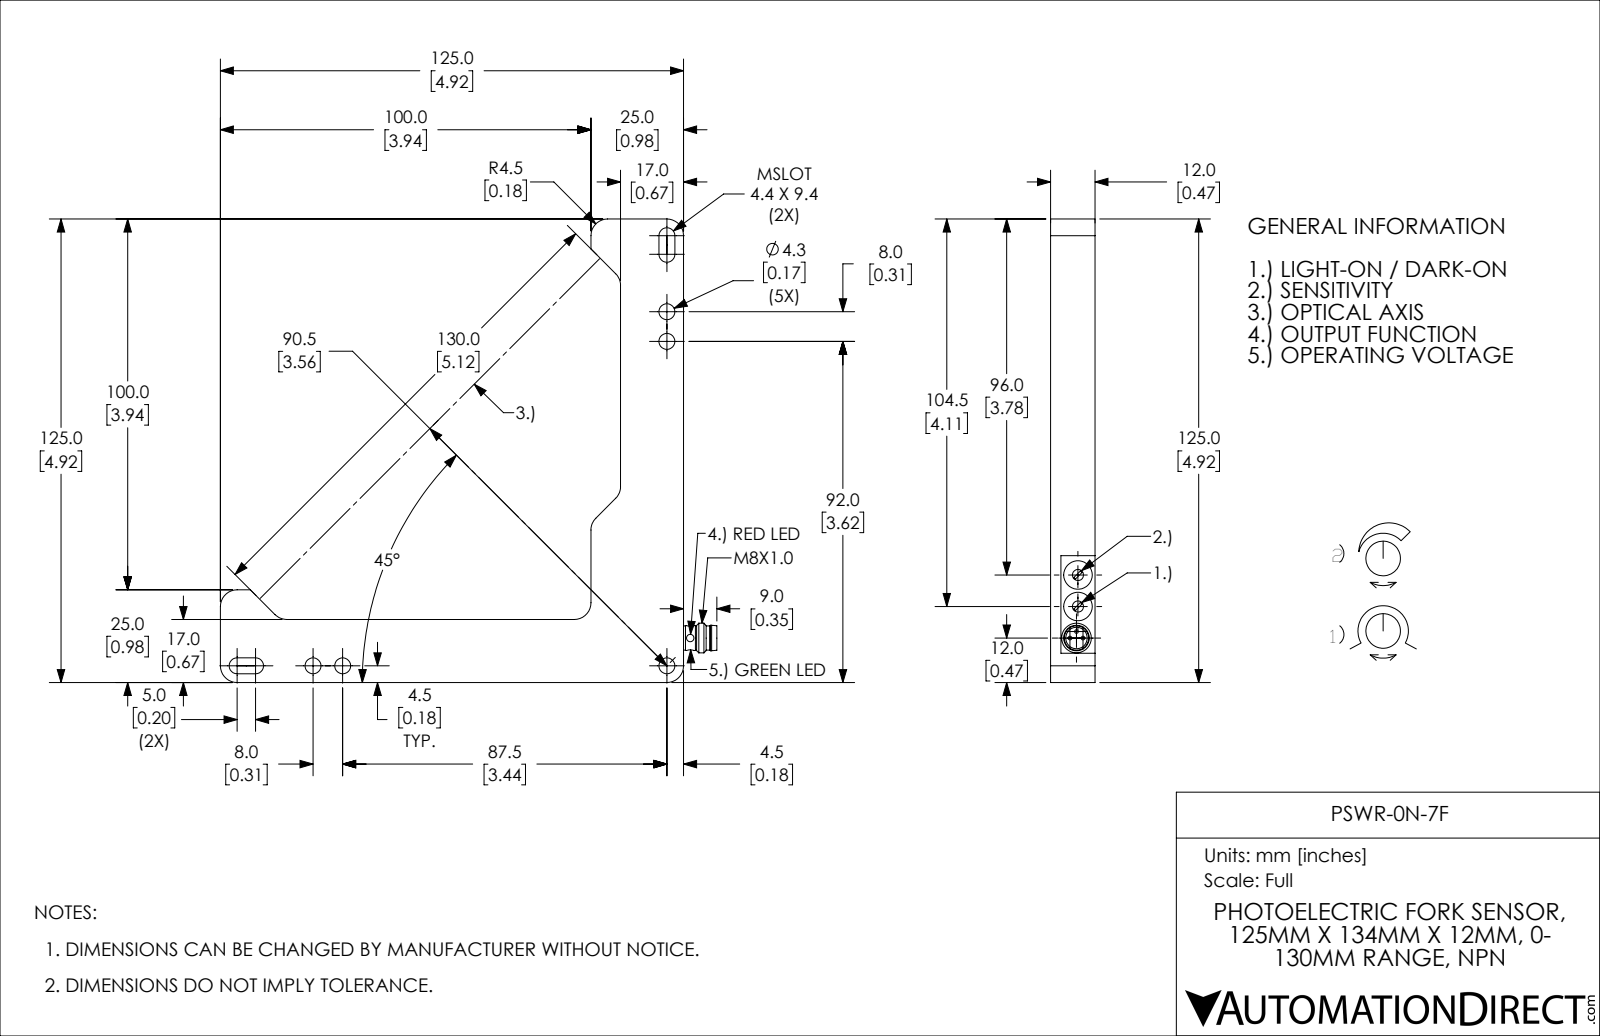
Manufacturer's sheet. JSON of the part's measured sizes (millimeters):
{"part_name": "PSWR-0N-7F", "step_written_by": "SolidWorks 2017 (AUTOMOTIVE_DESIGN)", "units": "millimeters", "bodies": {"solids": 1, "faces": 91, "planar": 43, "cylindrical": 41, "other": 7}, "overall_size": [134, 125, 12], "volume_mm3": 50980, "surface_area_mm2": 16280, "round_holes": [[4.3, 5], [2, 2], [3, 2], [7.7, 2], [5.8, 1]], "round_bosses_or_shafts": [[1, 3], [8, 1], [6.9, 1], [6.7, 1], [6.5, 1]], "partial_cylinders_radius": [[4.5, 10], [2.2, 4], [1.2, 2]], "face_to_face_distances": [12, 17, 125, 108, 25, 8, 100, 6.7, 10.3, 118.3], "hole_center_spacings": [8, 87.5, 95.5, 129.5, 8.5, 8.5, 9.8, 17]}
